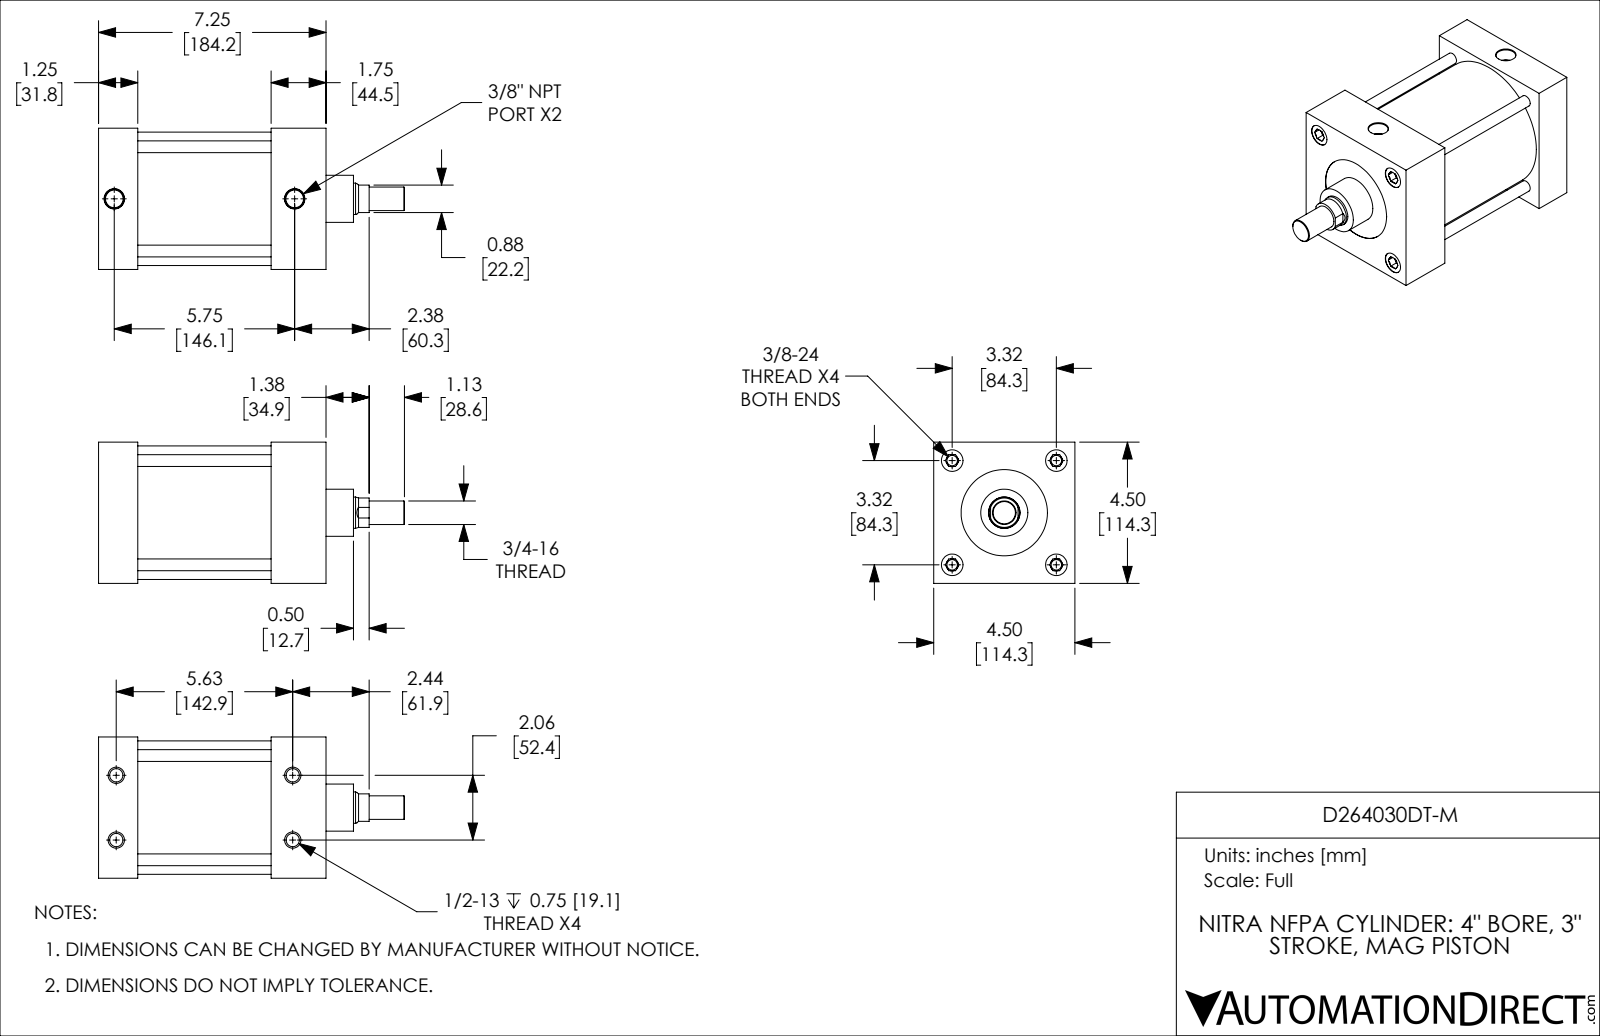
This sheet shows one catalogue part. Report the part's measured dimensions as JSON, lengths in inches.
{"part_name": "D264030DT-M_PISTON_KK1; D264030DT-M; D264030DT-M_BODY", "step_written_by": "SolidWorks 2019 (CONFIG_CONTROL_DESIGN)", "units": "inches", "bodies": {"solids": 2, "faces": 198, "planar": 58, "cylindrical": 62, "other": 78}, "overall_size": [9.75, 4.5, 4.5], "volume_in3": 87.58, "surface_area_in2": 354.4, "round_holes": [[0.332, 4], [0.422, 4], [0.687, 4], [0.562, 2], [1.001, 1], [2.75, 1], [4.001, 1]], "round_bosses_or_shafts": [[0.375, 4], [4.251, 1], [3.999, 1], [1.5, 1], [0.999, 1], [0.75, 1]], "partial_cylinders_radius": [[0.469, 1]], "face_to_face_distances": [1.25, 4.5, 4.25, 5.5, 7.25, 6, 1.75, 2.5, 3, 4.75], "hole_center_spacings": [2.347, 3.32, 1.033, 5.78, 4.695, 5.625, 1.034, 2.062]}
